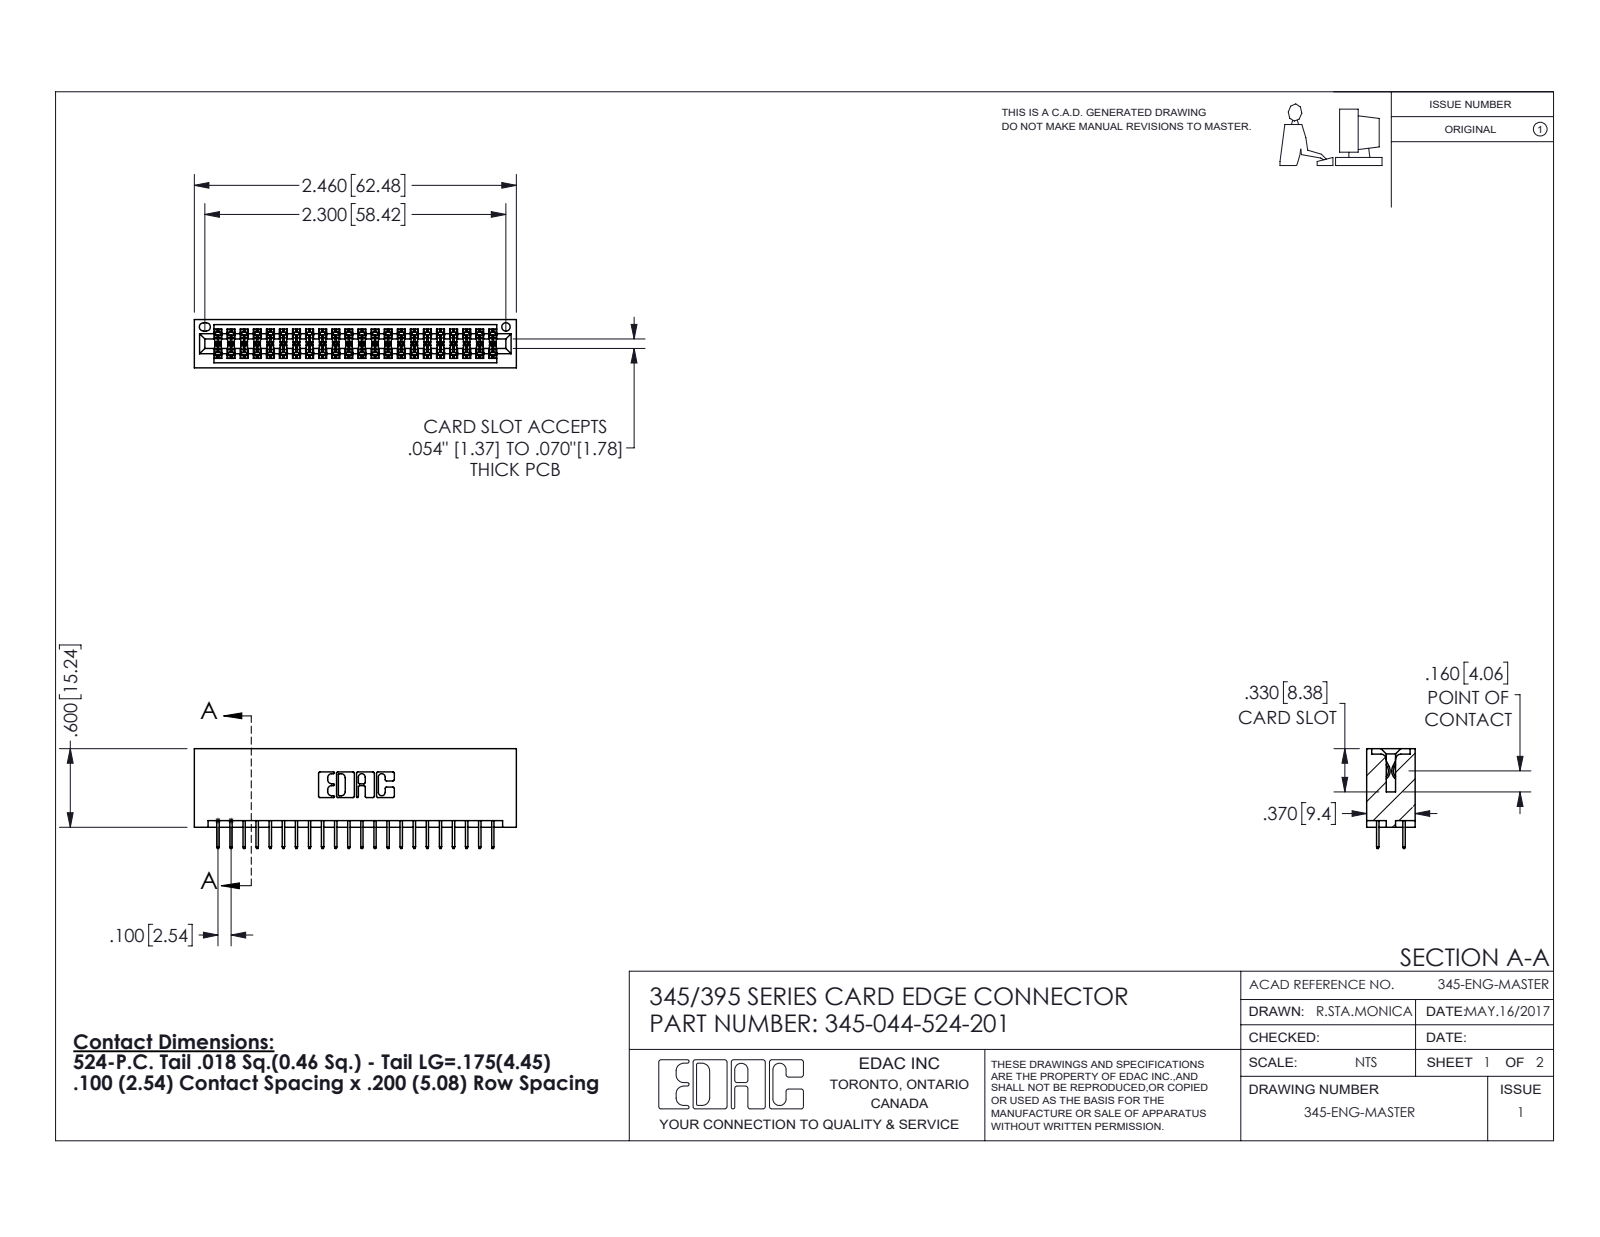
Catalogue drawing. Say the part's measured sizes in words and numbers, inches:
The part is named "345 Part_No Mounting Lugs; 345-292-001_345-293-124; 345-044-524-201". Its 3-D file was written by "SolidWorks 2016 (CONFIG_CONTROL_DESIGN)". It is 45 solids with 2494 faces: 1792 planar, 702 cylindrical and 0 other. Overall it measures 2.46 by 0.762 by 0.37 inches. Its volume is 0.393 cubic inches and its surface area 14.34 square inches. Round holes: 1 of diameter 0.064. Partial cylindrical surfaces (rounded edges, fillets, slot ends): 66 of radius 0.006, 22 of radius 0.01, 6 of radius 0.007, 6 of radius 0.031, 3 of radius 0.026, 2 of radius 0.014, 2 of radius 0.019, 2 of radius 0.022. The main face-to-face distances are 0.298, 0.072, 0.2, 0.37, 0.098, 0.272, 0.025, 0.225, 0.072, 0.1.
